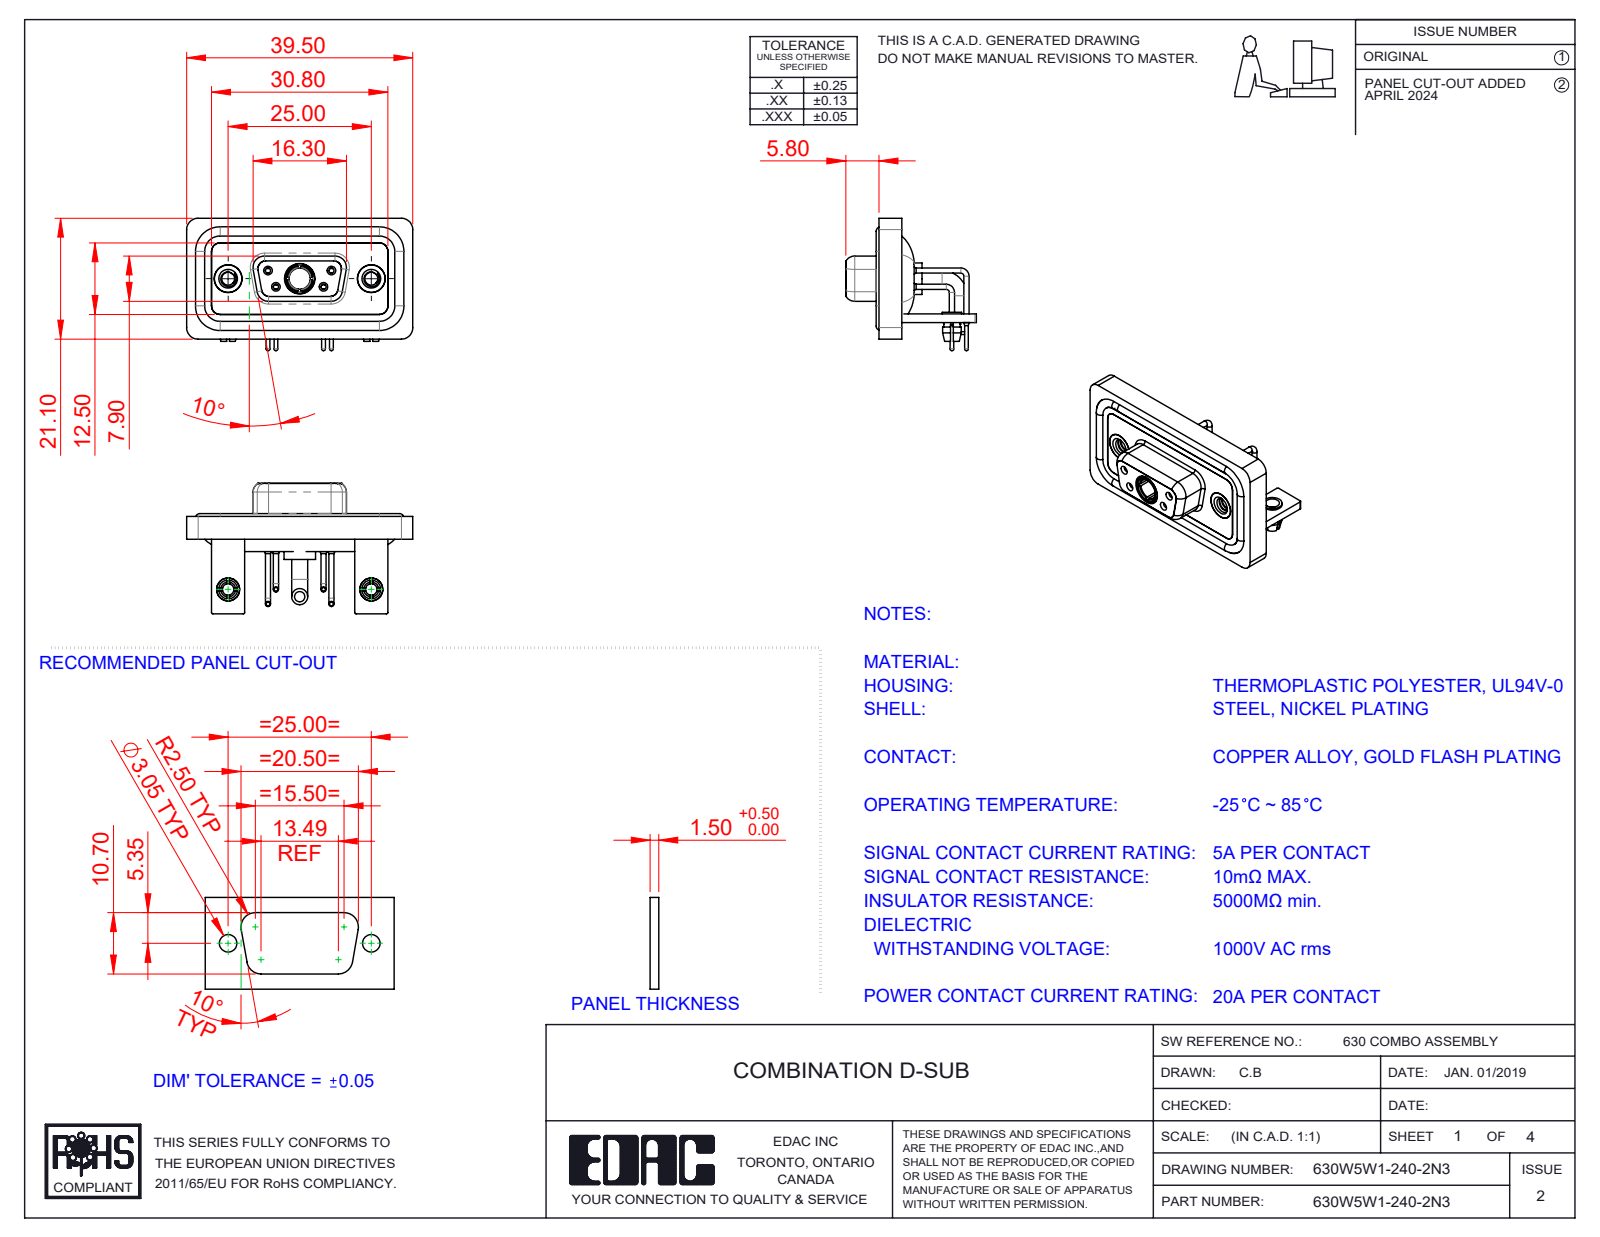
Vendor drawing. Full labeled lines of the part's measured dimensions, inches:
Part name (STEP PRODUCT): 630Combo Threaded Rivet_2; 630Combo Waterproof Housing_09 Contacts; 630Combo Contact Row 1_50 Contacts; Power Socket_20A RA (+7 more)
STEP written by: SolidWorks 2023 (CONFIG_CONTROL_DESIGN)
Units: inches
Bodies: 17 solids, 816 faces (262 planar, 361 cylindrical, 193 other)
Overall size (bounding box): 1.555 × 0.91 × 0.898
Volume: 0.319 in³ · Surface area: 13.62 in²
Round holes (diameter × count): ⌀0.079 ×6, ⌀0.035 ×4, ⌀0.043 ×4, ⌀0.059 ×4, ⌀0.191 ×3, ⌀0.063 ×2, ⌀0.067 ×2, ⌀0.089 ×2, ⌀0.098 ×2, ⌀0.126 ×2, ⌀0.157 ×2, ⌀0.159 ×2
Round bosses / shafts (diameter × count): ⌀0.063 ×6, ⌀0.035 ×4, ⌀0.026 ×4, ⌀0.195 ×2, ⌀0.189 ×2, ⌀0.157 ×2, ⌀0.134 ×2, ⌀0.13 ×2
Partial cylindrical surfaces — rounded edges, fillets, slot ends (radius × count): R0.079 ×19, R0.059 ×18, R0.01 ×16, R0.053 ×8, R0.063 ×8, R0.02 ×5, R0.024 ×4, R0.026 ×4
Main face-to-face distances: 0.016, 0.114, 0.059, 0.071, 0.043, 0.146, 0.063, 0.031, 0.098, 0.122
Hole centre spacings: 0.124, 0.225, 0.28, 0.492, 0.713, 0.984, 0.173, 0.173
